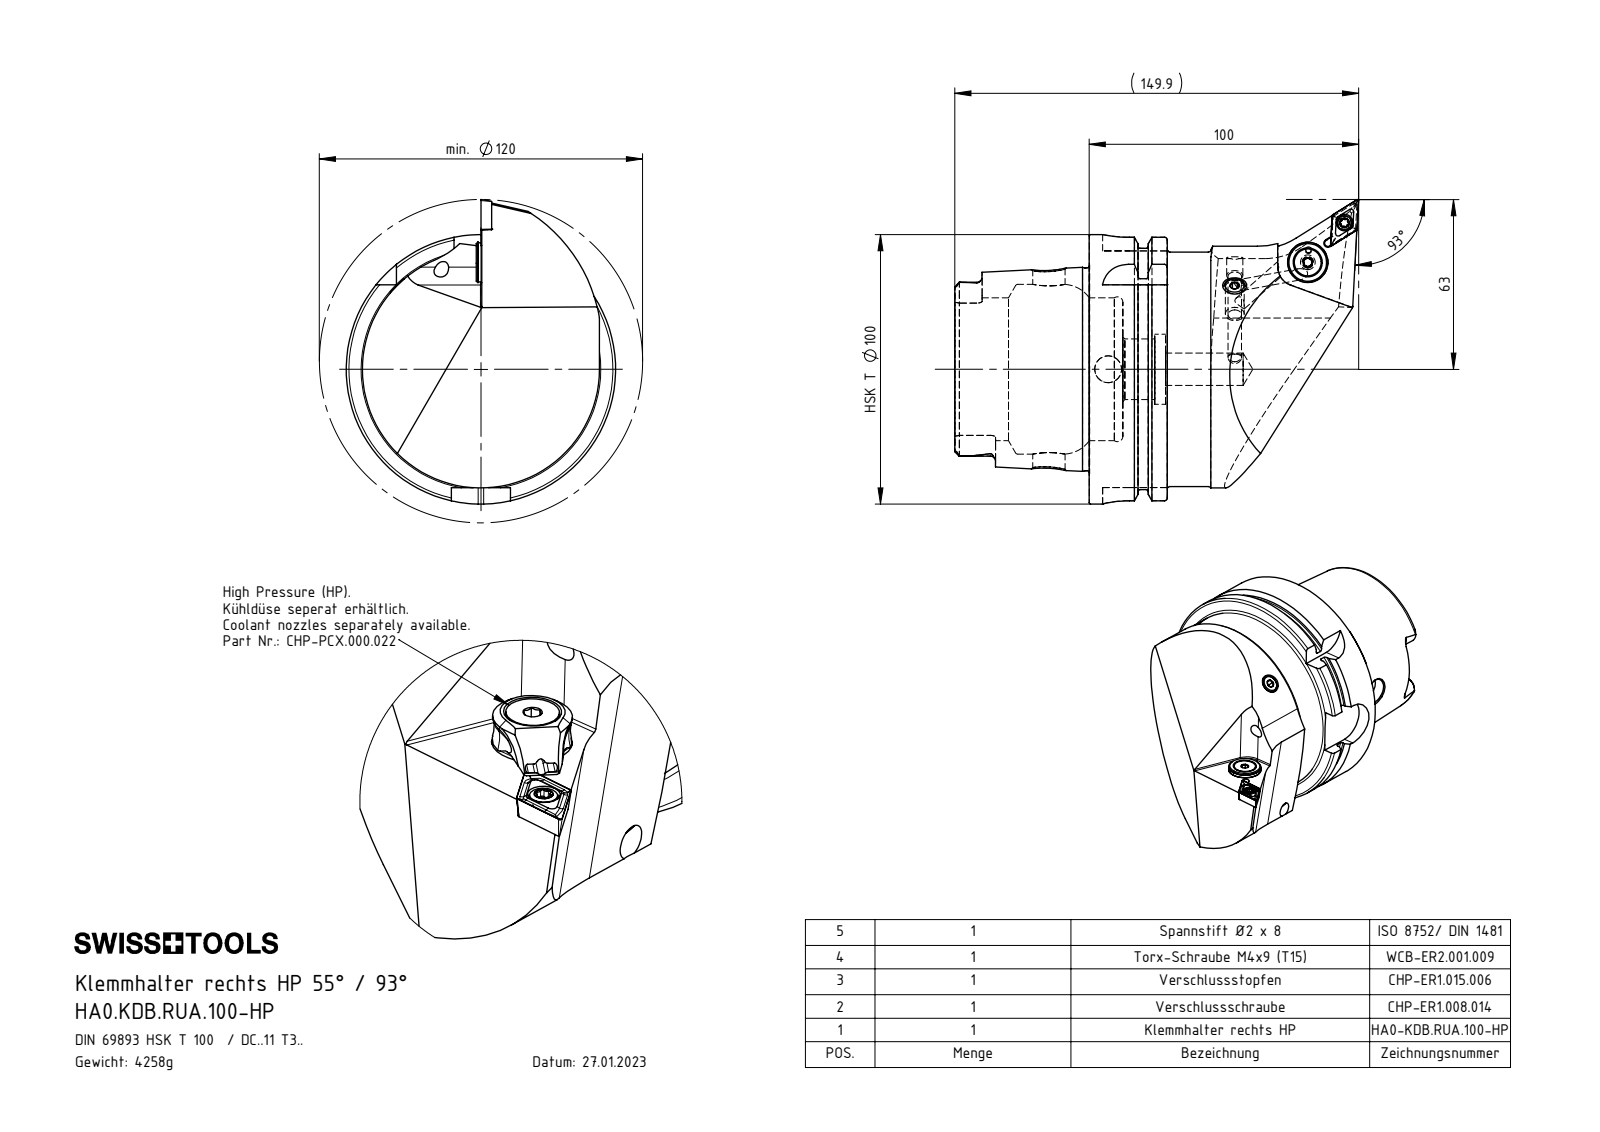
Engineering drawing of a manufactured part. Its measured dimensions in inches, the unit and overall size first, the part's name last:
Units: inches
Overall size (bounding box): 5.902 × 4.449 × 3.937
Round holes (diameter × count): ⌀0.197 ×4, ⌀0.165 ×2, ⌀0.472 ×2, ⌀0.047 ×1, ⌀0.079 ×1, ⌀0.098 ×1, ⌀0.118 ×1, ⌀0.13 ×1, ⌀0.173 ×1, ⌀0.205 ×1, ⌀0.236 ×1, ⌀0.24 ×1
Round bosses / shafts (diameter × count): ⌀3.937 ×1, ⌀3.62 ×1, ⌀3.425 ×1, ⌀2.963 ×1, ⌀0.591 ×1, ⌀0.528 ×1, ⌀0.394 ×1, ⌀0.315 ×1
Partial cylindrical surfaces — rounded edges, fillets, slot ends (radius × count): R0.013 ×6, R0.023 ×6, R0.075 ×6, R0.394 ×4, R0.02 ×2, R0.19 ×2, R0.192 ×2, R0.049 ×1
Main face-to-face distances: 0.49, 1.14, 0.65, 1.965, 2.455, 3.104, 3.457, 1.72, 3.079, 1.114
Hole centre spacings: 0.177, 0.662, 0.666, 0.788, 0.793, 3.31, 3.405, 4.063
Volume: 33.1 in³ · Surface area: 109.6 in²
Bodies: 10 solids, 447 faces (116 planar, 129 cylindrical, 202 other)
Part name (STEP PRODUCT): CHP-ER1.015.006; DIN 7991 - M5x15; CHP-ER1.008.014_A; HA0-KDB.RUA.100-HP_A_Fertigbearbeitung (+7 more)
STEP written by: SolidWorks 2017 (AUTOMOTIVE_DESIGN)
